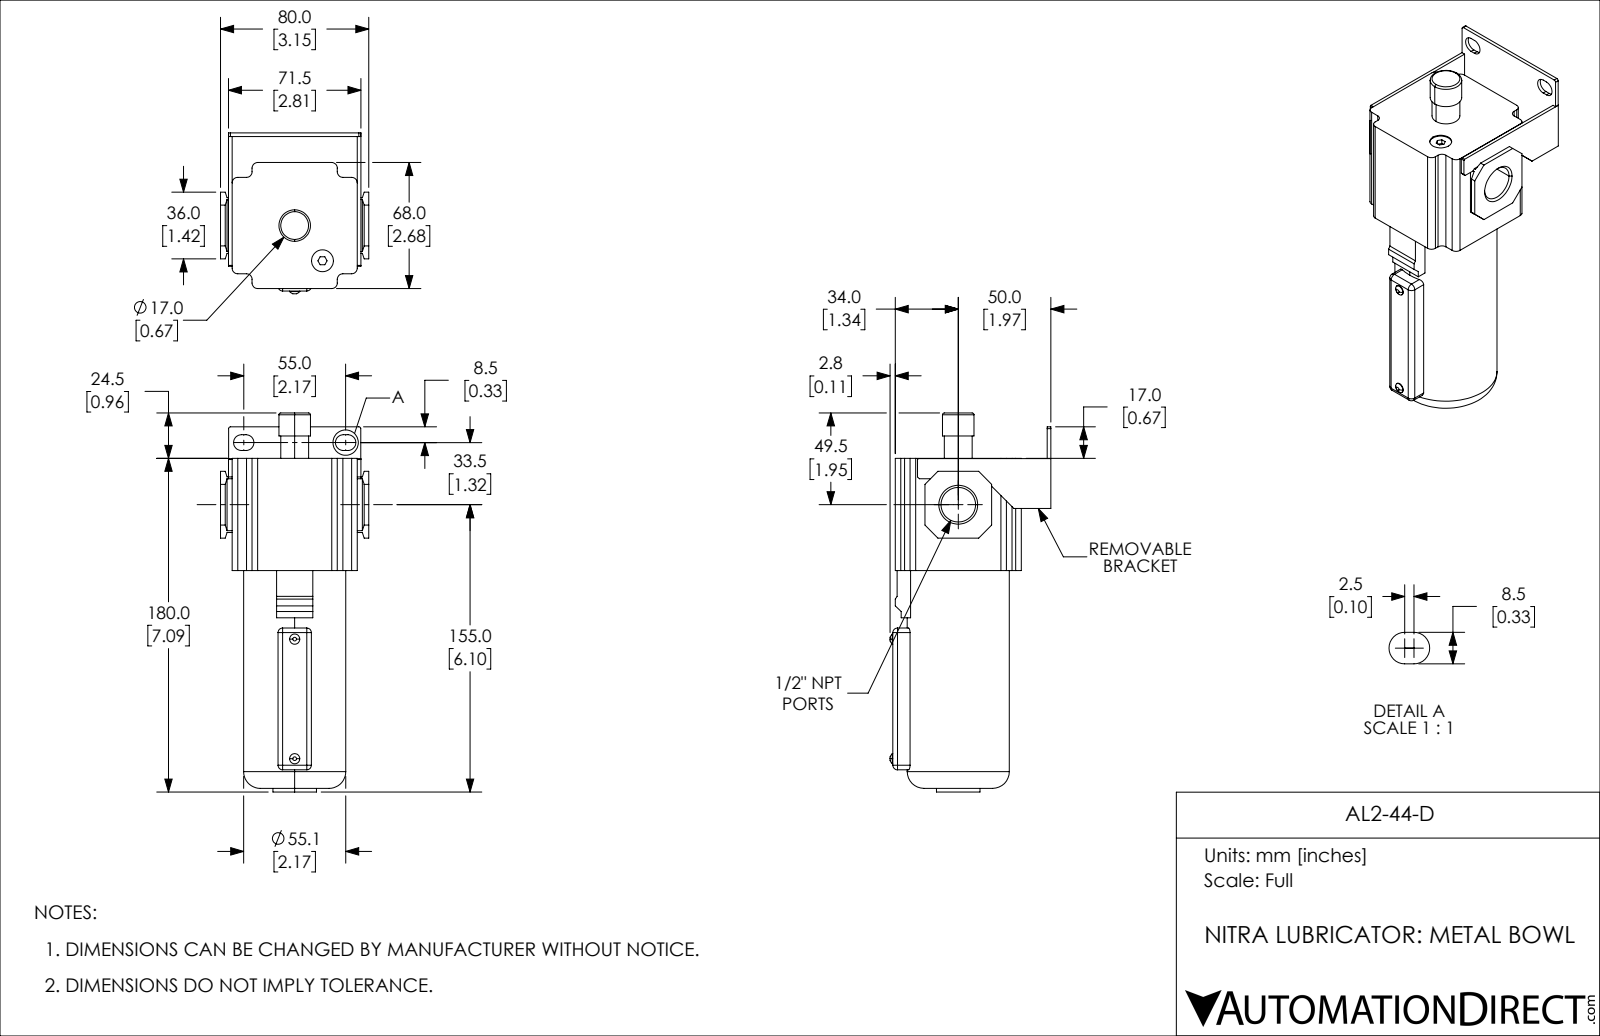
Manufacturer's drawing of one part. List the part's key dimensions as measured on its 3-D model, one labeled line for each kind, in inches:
Part name (STEP PRODUCT): AL2-44-D
STEP written by: SolidWorks 2019 (CONFIG_CONTROL_DESIGN)
Units: inches
Bodies: 1 solid, 163 faces (103 planar, 44 cylindrical, 16 other)
Overall size (bounding box): 8.051 × 3.417 × 3.15
Volume: 34.52 in³ · Surface area: 94.94 in²
Round holes (diameter × count): ⌀0.465 ×1, ⌀0.733 ×1
Round bosses / shafts (diameter × count): ⌀0.217 ×2, ⌀2.169 ×1, ⌀0.925 ×1, ⌀0.669 ×1, ⌀0.591 ×1
Partial cylindrical surfaces — rounded edges, fillets, slot ends (radius × count): R0.118 ×12, R0.098 ×8, R0.167 ×4, R0.039 ×2
Main face-to-face distances: 0.079, 0.551, 0.63, 3.228, 2.677, 3.307, 2.736, 2.657, 2.382, 0.167
